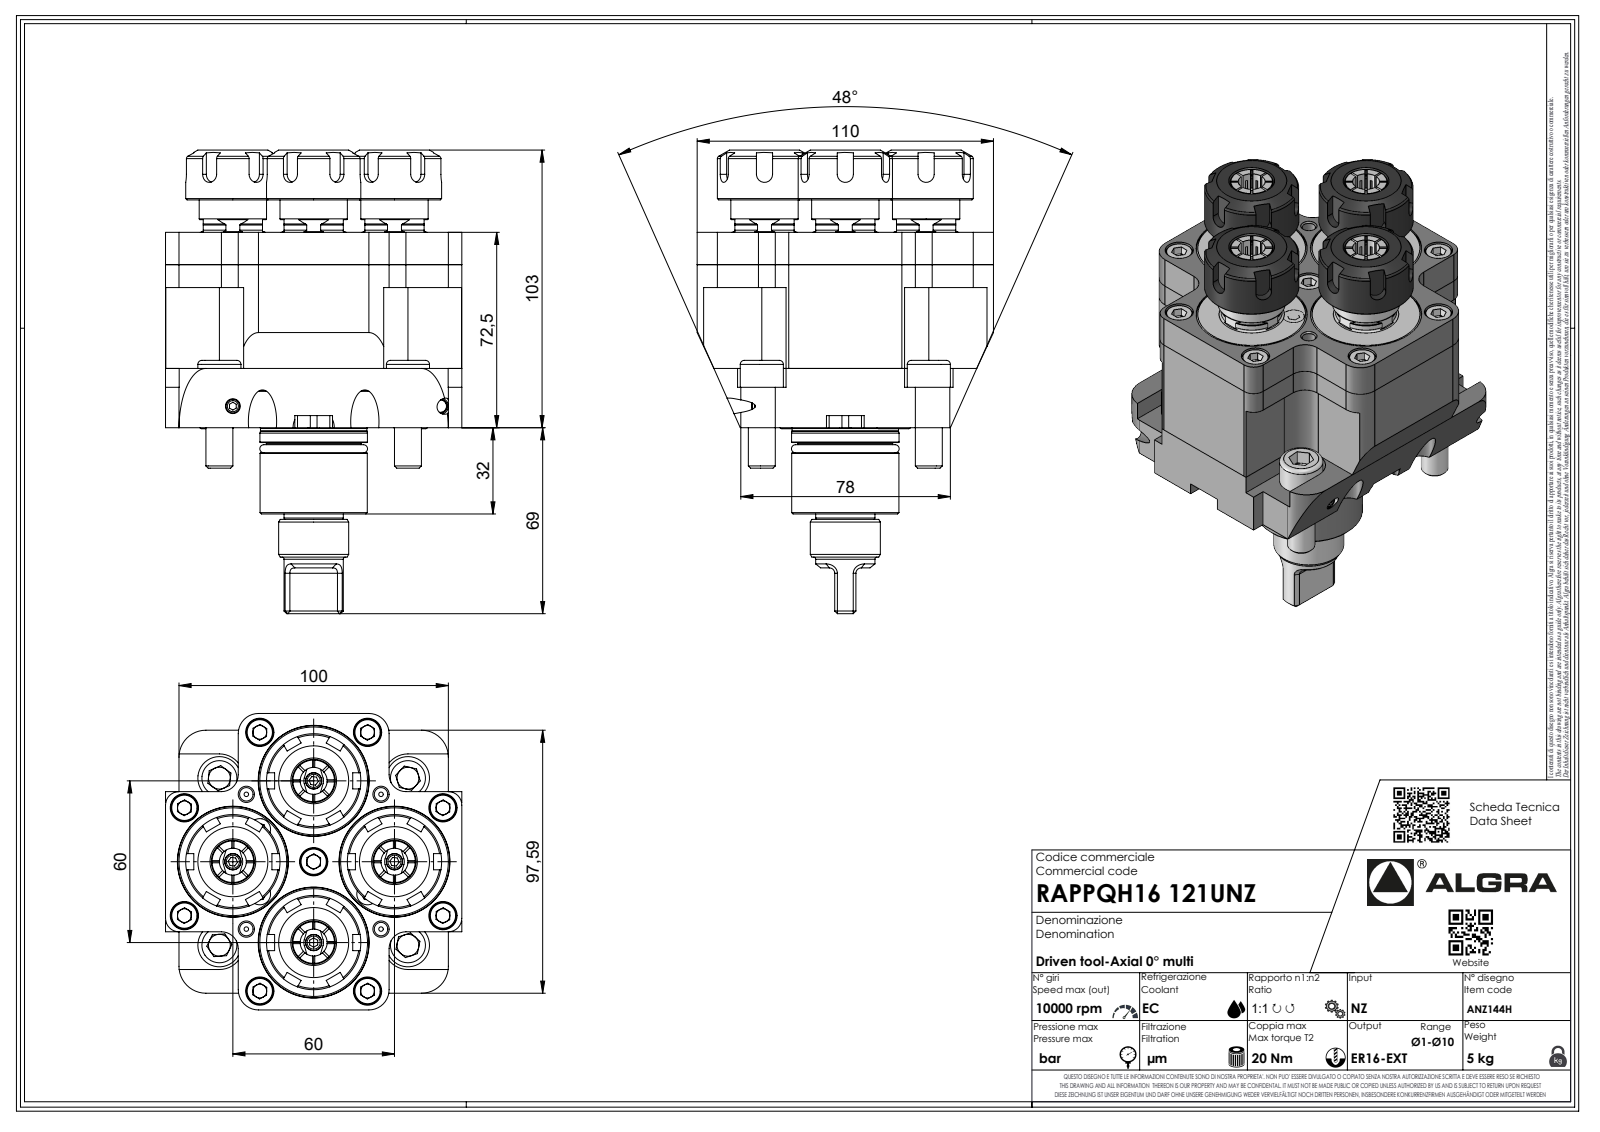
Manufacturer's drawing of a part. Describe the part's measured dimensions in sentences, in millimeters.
The part is named "RAPPQH16121UNZ". Its 3-D file was written by "SolidWorks 2023 (AUTOMOTIVE_DESIGN)". It is 1 solid with 834 faces: 503 planar, 180 cylindrical and 151 other. Overall it measures 172.02 by 110 by 110 millimeters. Its volume is 762 611 cubic millimeters and its surface area 103 090 square millimeters. Round holes: 4 of diameter 29.2, 4 of diameter 33.2, 4 of diameter 37.2, 4 of diameter 41.2, 1 of diameter 2.1. Round bosses or shafts: 4 of diameter 41, 4 of diameter 37, 4 of diameter 35, 4 of diameter 33, 4 of diameter 29, 4 of diameter 25, 4 of diameter 16, 4 of diameter 10. Partial cylindrical surfaces (rounded edges, fillets, slot ends): 20 of radius 5, 11 of radius 3, 7 of radius 0.33, 7 of radius 0.52, 7 of radius 3.7, 4 of radius 6.25, 4 of radius 7.5, 4 of radius 9. The main face-to-face distances are 29, 72.5, 4, 110, 81, 33, 65.5, 4.5, 77, 52. The hole center spacings are 42.43, 60.
